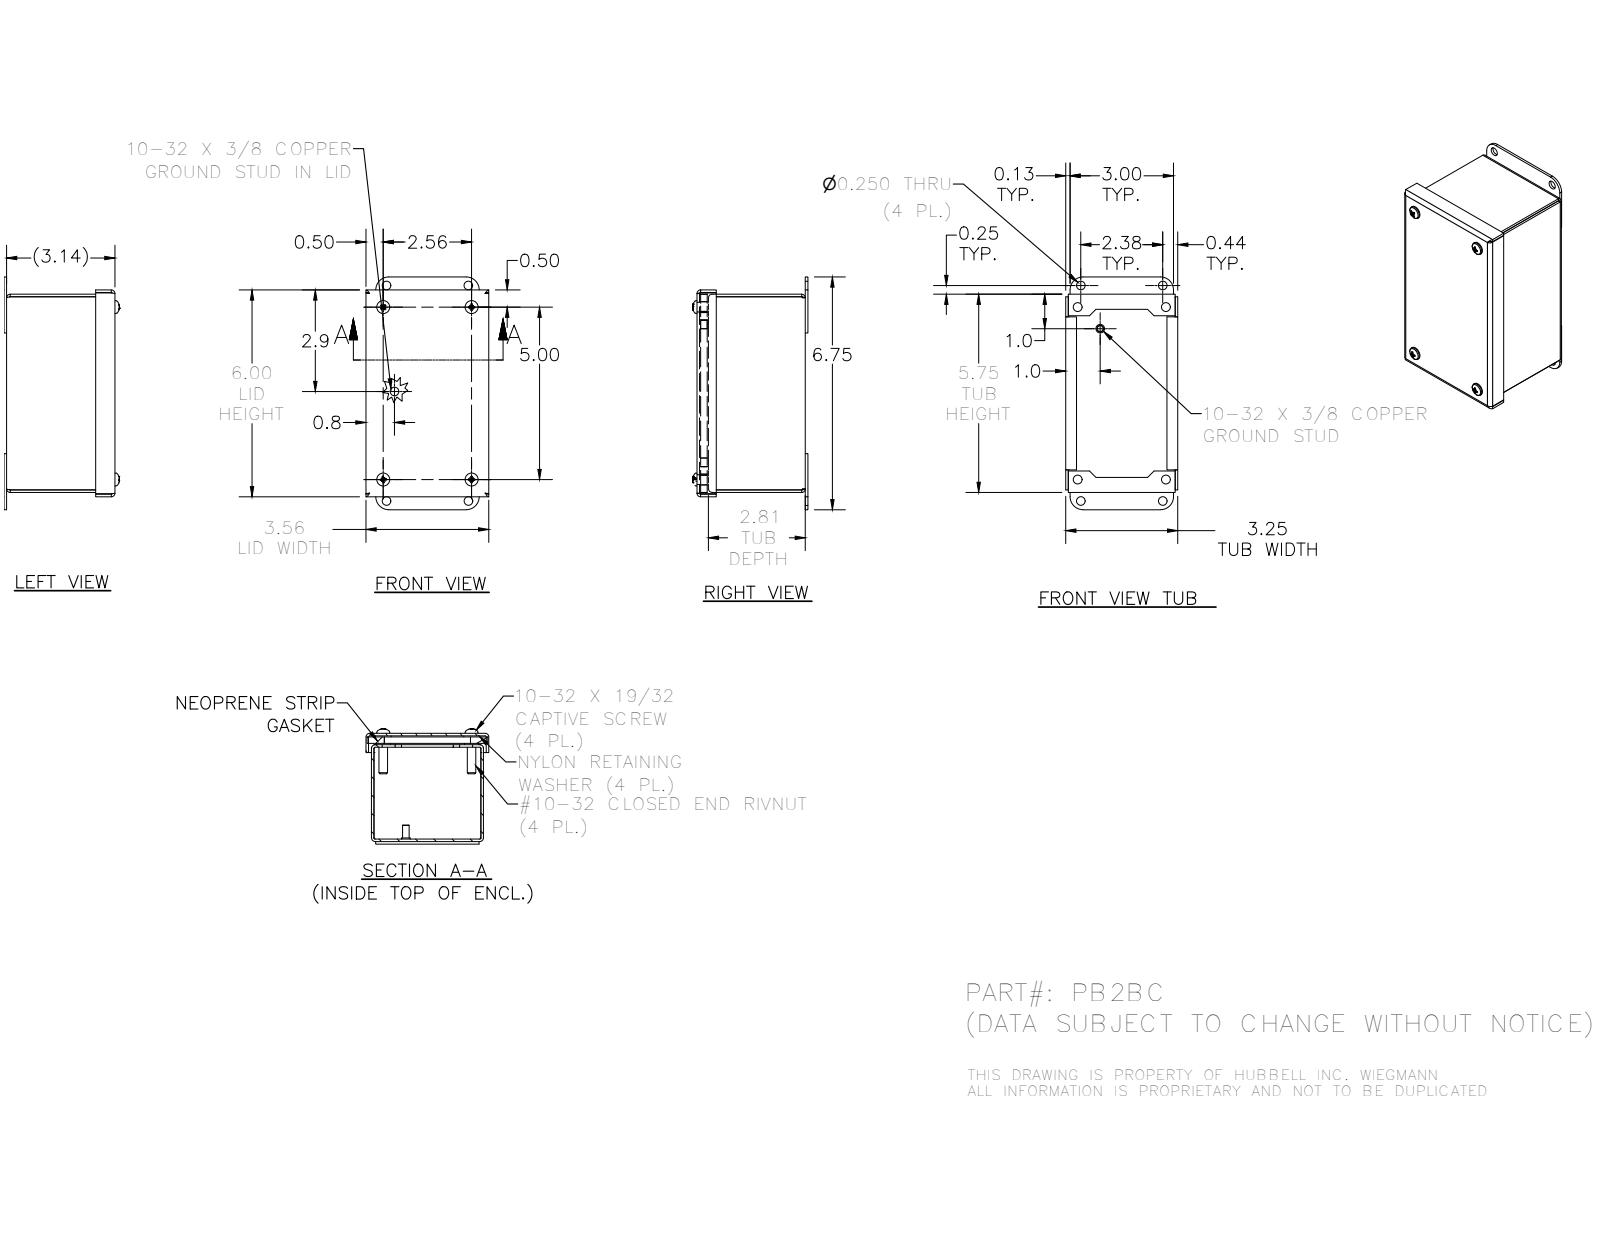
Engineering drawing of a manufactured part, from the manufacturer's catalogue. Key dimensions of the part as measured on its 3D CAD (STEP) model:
Part name (STEP PRODUCT): 39077; 316232; 372163; PB2BCBKP (+5 more)
STEP written by: Autodesk Inventor 2016 (AUTOMOTIVE_DESIGN)
Units: millimetres
Bodies: 20 solids, 488 faces (278 planar, 96 cylindrical, 114 other)
Overall size (bounding box): 171.45 × 90.49 × 84.99
Volume: 165 547 mm³ · Surface area: 168 477 mm²
Round holes (diameter × count): ⌀3.96 ×4, ⌀4.98 ×4, ⌀6.35 ×4, ⌀6.53 ×4, ⌀7.06 ×4, ⌀7.14 ×4, ⌀7.95 ×4
Round bosses / shafts (diameter × count): ⌀4.83 ×6, ⌀11.51 ×4, ⌀10.31 ×4, ⌀9.47 ×4, ⌀6.3 ×4, ⌀6.35 ×2
Partial cylindrical surfaces — rounded edges, fillets, slot ends (radius × count): R0.79 ×12, R2.67 ×12, R2.27 ×4, R9.53 ×4
Main face-to-face distances: 1.88, 77.93, 80.67, 79.81, 76.05, 82.55, 78.79, 0.81, 4.78, 2.69
Hole centre spacings: 127, 142.69, 142.7, 16.05, 126.98, 142.89, 142.9, 156.02
